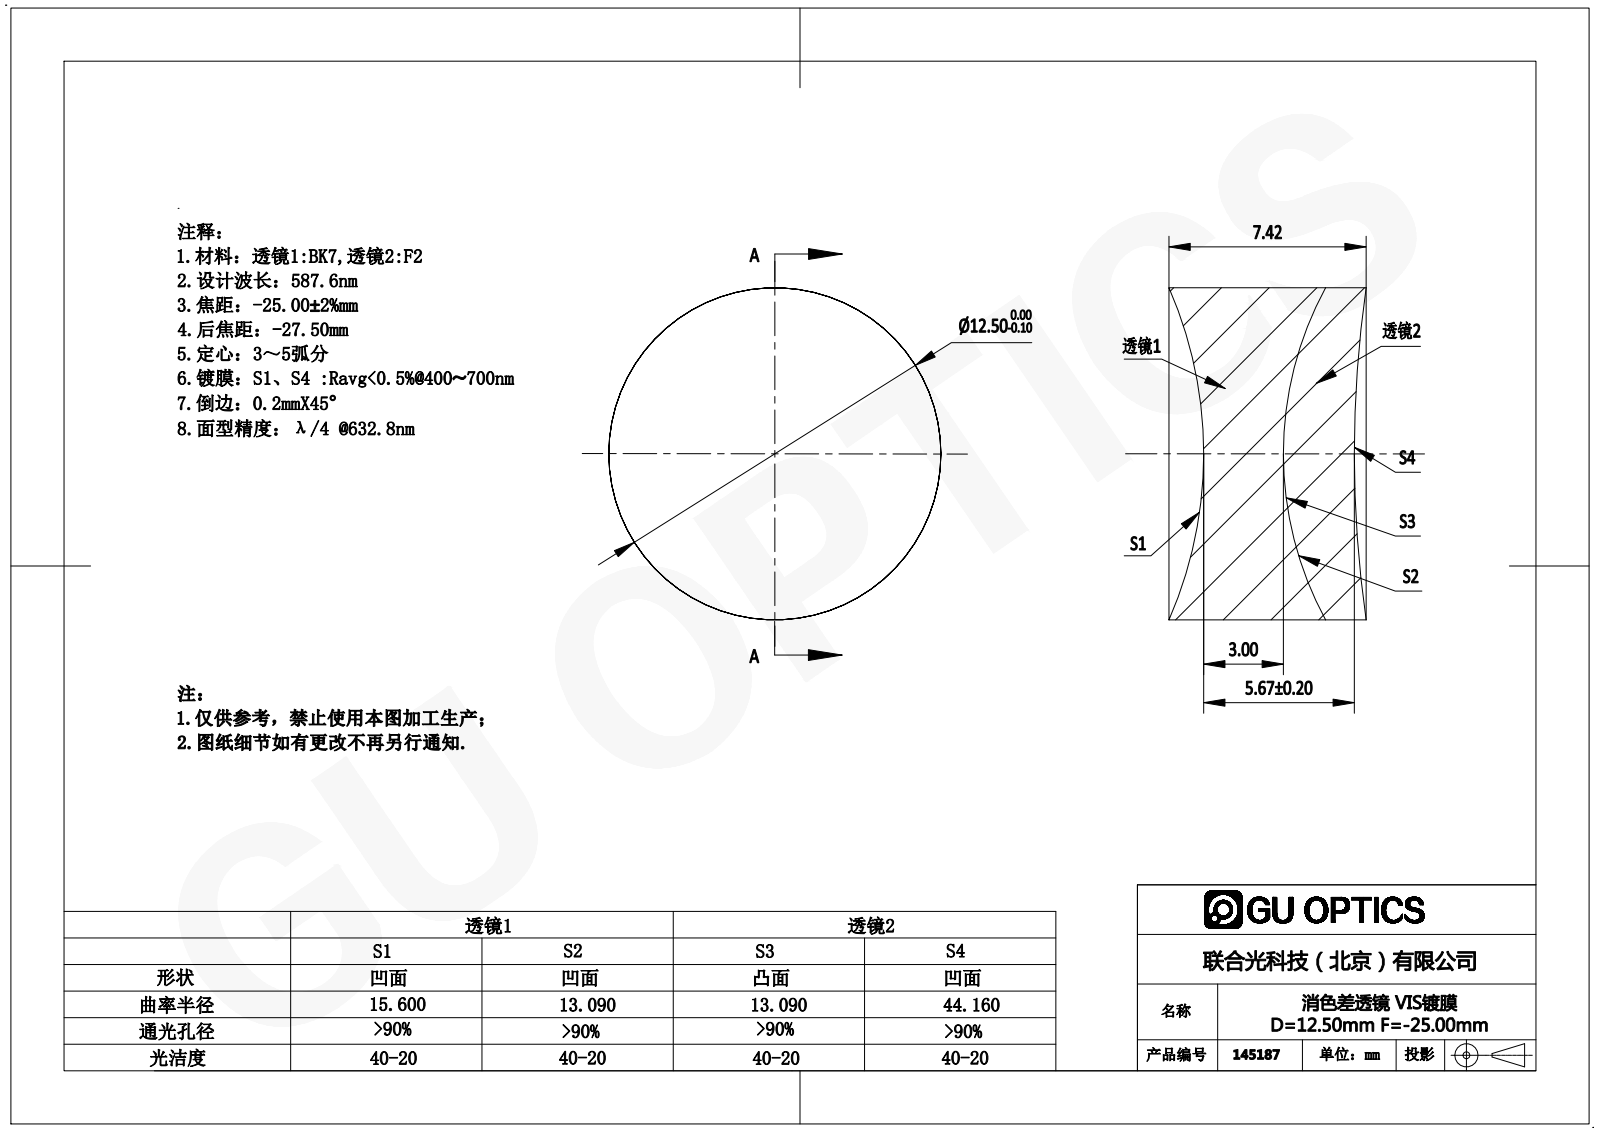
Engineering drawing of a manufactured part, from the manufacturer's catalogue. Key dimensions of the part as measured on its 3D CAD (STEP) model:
Part name (STEP PRODUCT): 145187
STEP written by: SolidWorks 2016 (AUTOMOTIVE_DESIGN)
Units: millimetres
Bodies: 2 solids, 12 faces (0 planar, 4 cylindrical, 8 other)
Overall size (bounding box): 12.5 × 12.5 × 7.42
Volume: 802 mm³ · Surface area: 804 mm²
Round bosses / shafts (diameter × count): ⌀12.5 ×1
